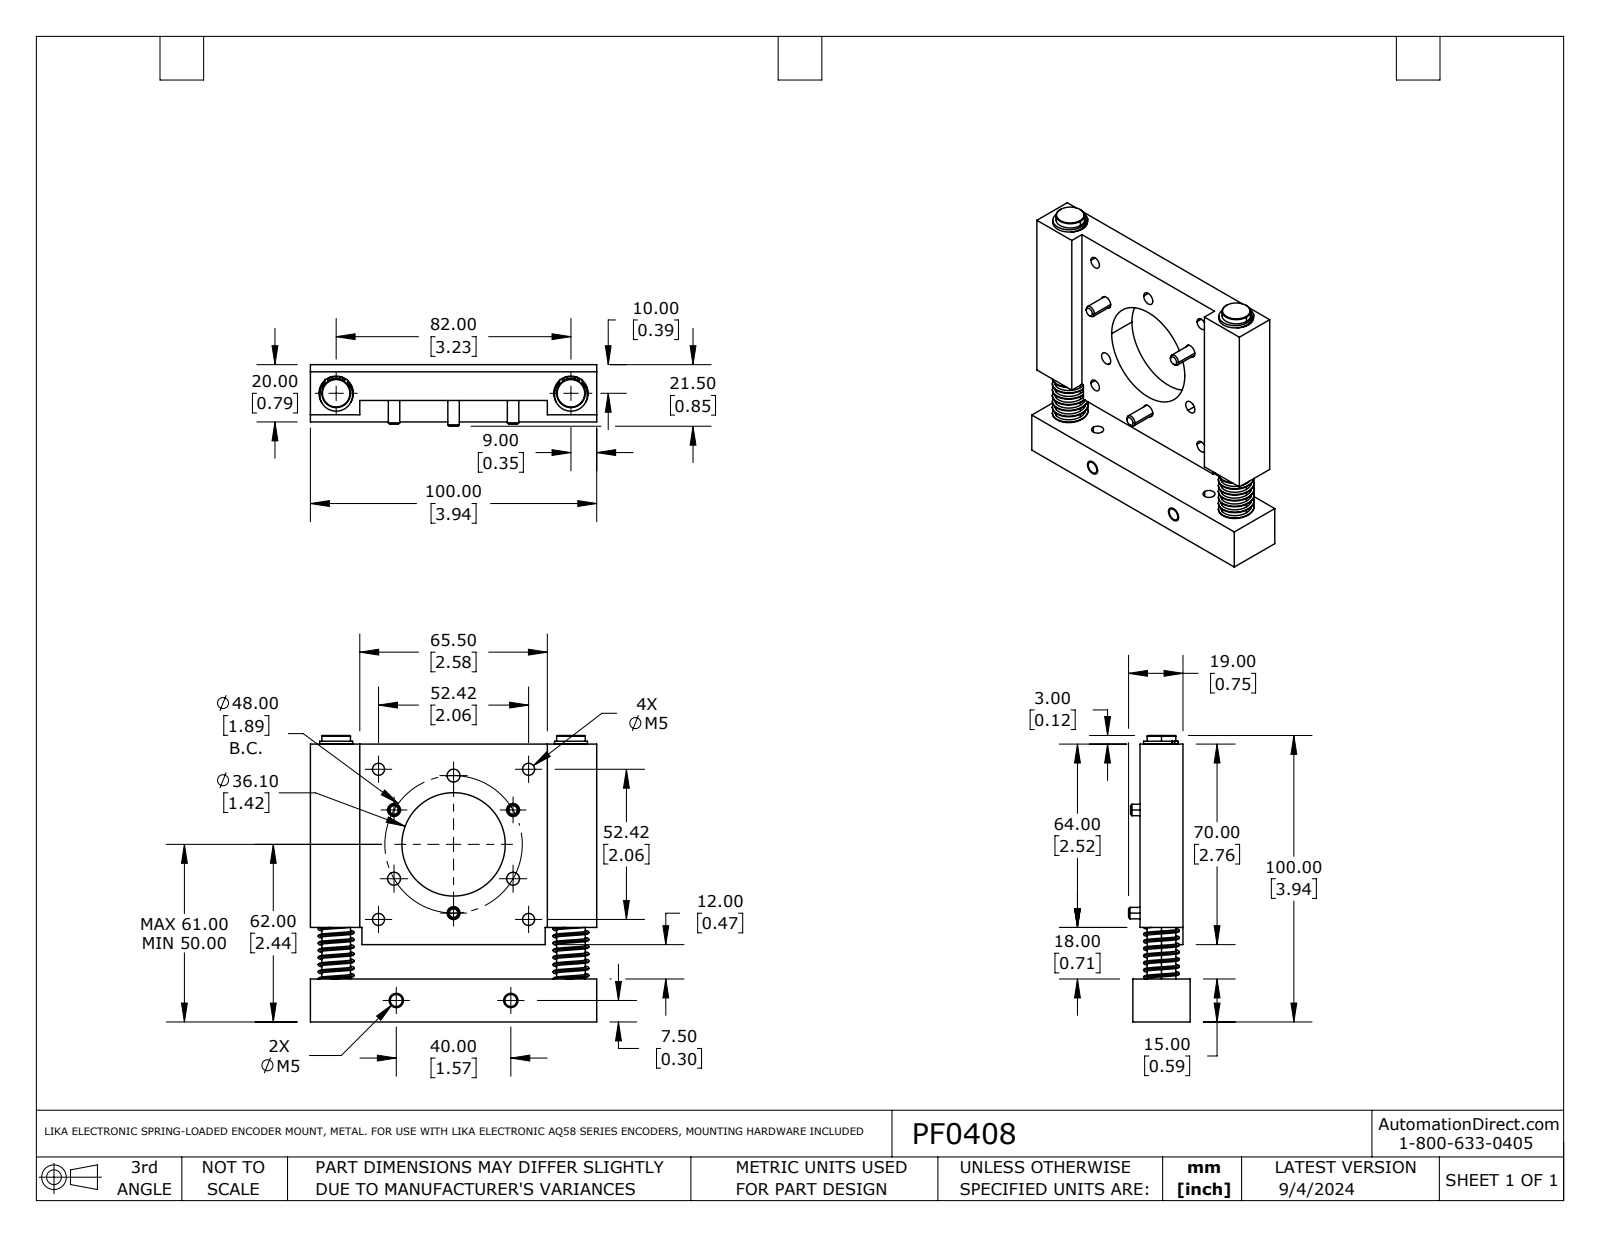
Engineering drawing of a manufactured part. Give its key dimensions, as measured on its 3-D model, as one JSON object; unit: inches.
{"part_name": "PF0408", "step_written_by": "SolidWorks 2021 (AUTOMOTIVE_DESIGN)", "units": "inches", "bodies": {"solids": 6, "faces": 391, "planar": 105, "cylindrical": 172, "other": 114}, "overall_size": [3.937, 3.937, 0.846], "volume_in3": 5.974, "surface_area_in2": 59.75, "round_holes": [[0.165, 8], [0.315, 8], [0.177, 6], [0.039, 4], [0.472, 2], [1.421, 1]], "round_bosses_or_shafts": [[0.157, 3], [0.394, 2], [0.354, 2], [0.197, 2]], "partial_cylinders_radius": [[0.008, 17], [0.007, 9], [0.02, 2], [0.226, 2], [0.255, 2]], "face_to_face_distances": [0.591, 0.394, 0.098, 0.689, 0.197, 0.295, 0.492, 0.787, 3.937, 3.228], "hole_center_spacings": [0.945, 0.208, 0.599, 1.035, 1.459, 1.519, 1.637, 1.933]}
